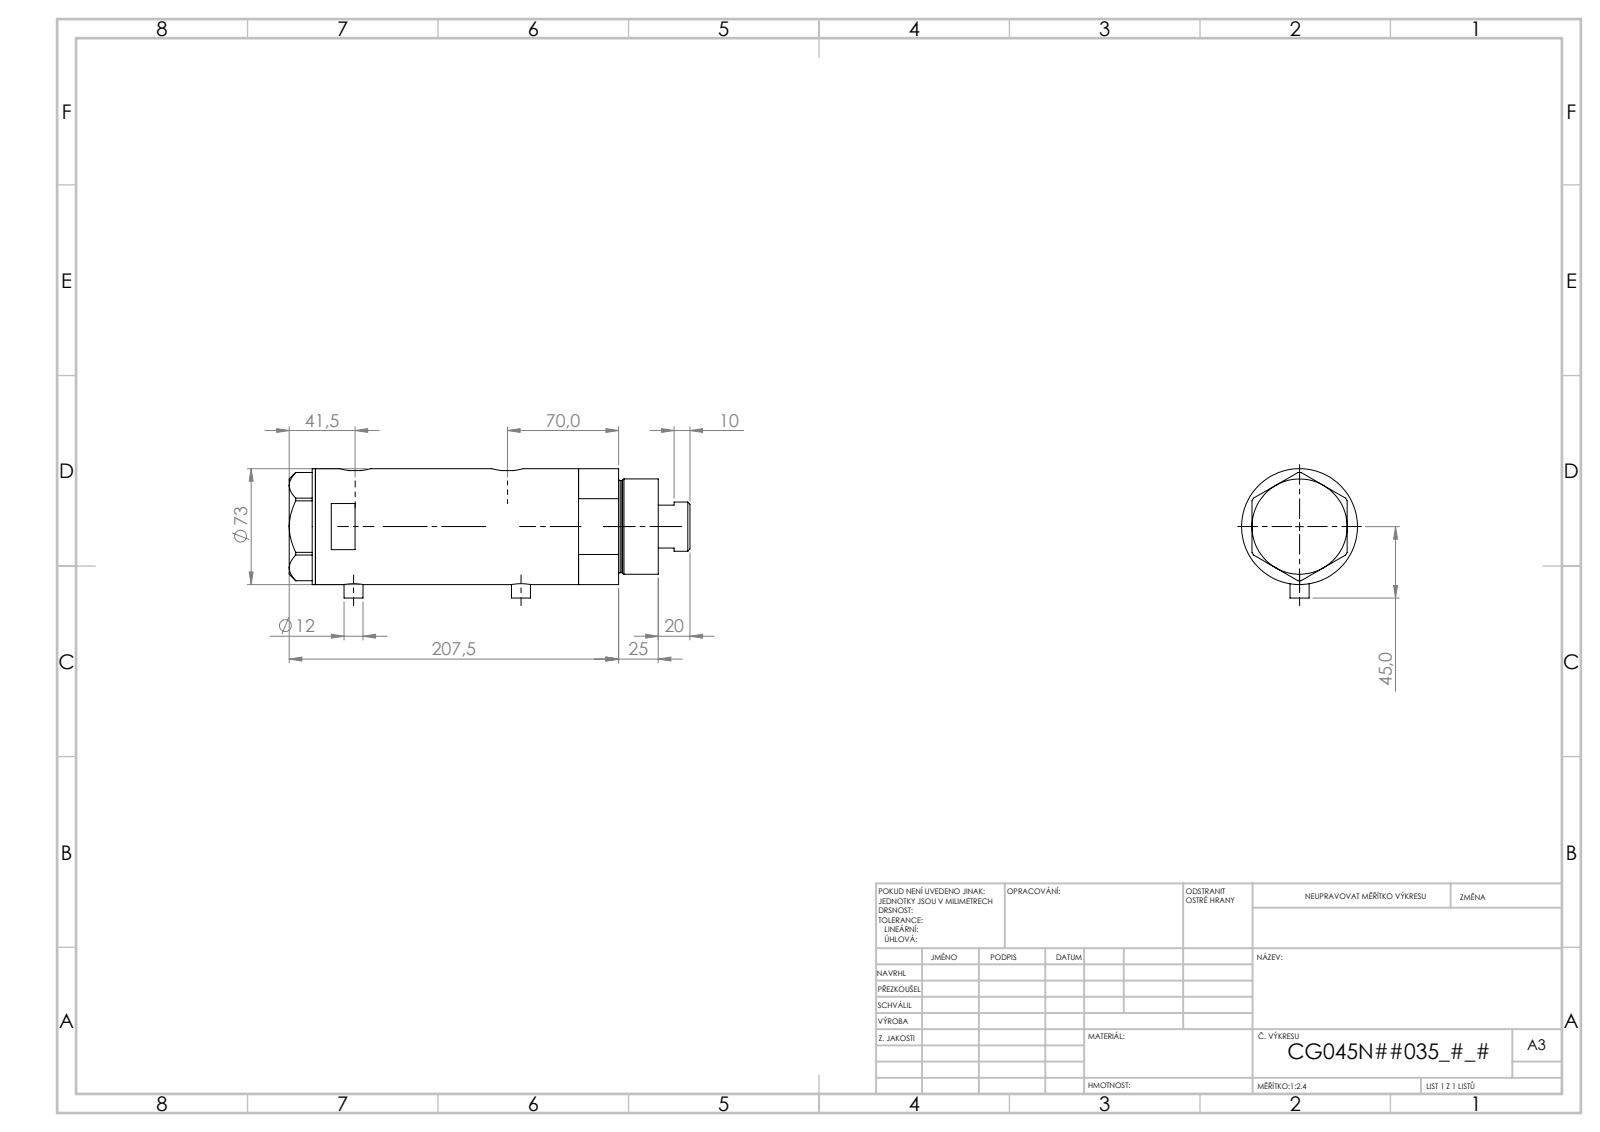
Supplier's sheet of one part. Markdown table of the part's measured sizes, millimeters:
| quantity | value |
| --- | --- |
| part name | V270CG_FRONT; V270CG_BACK; V270CG_VC; V270CG_MIDDLE |
| STEP written by | SolidWorks 2019 (CONFIG_CONTROL_DESIGN) |
| units | millimeters |
| bodies | 4 solids, 125 faces (50 planar, 55 cylindrical, 20 other) |
| overall size | 226.52 × 74.1 × 73 |
| volume | 785 728 mm³ |
| surface area | 136 434 mm² |
| round holes (diameter × count) | 5 × 2, 12.5 × 2, 13.16 × 2, 10.5 × 1, 32 × 1, 33.5 × 1, 45 × 1, 48 × 1, 64 × 1 |
| round bosses / shafts (diameter × count) | 12 × 2, 73 × 1, 60 × 1, 58 × 1, 31 × 1 |
| partial cylindrical surfaces (radius × count) | 10 × 2 |
| main face-to-face distances | 76.15, 16.5, 118.64, 102.14, 190.01, 87.87, 164.02, 42.5, 26, 76.14 |
| hole center spacings | 86.65, 0.99, 1, 8.5, 8.51, 77.15, 78.14, 78.15 |
